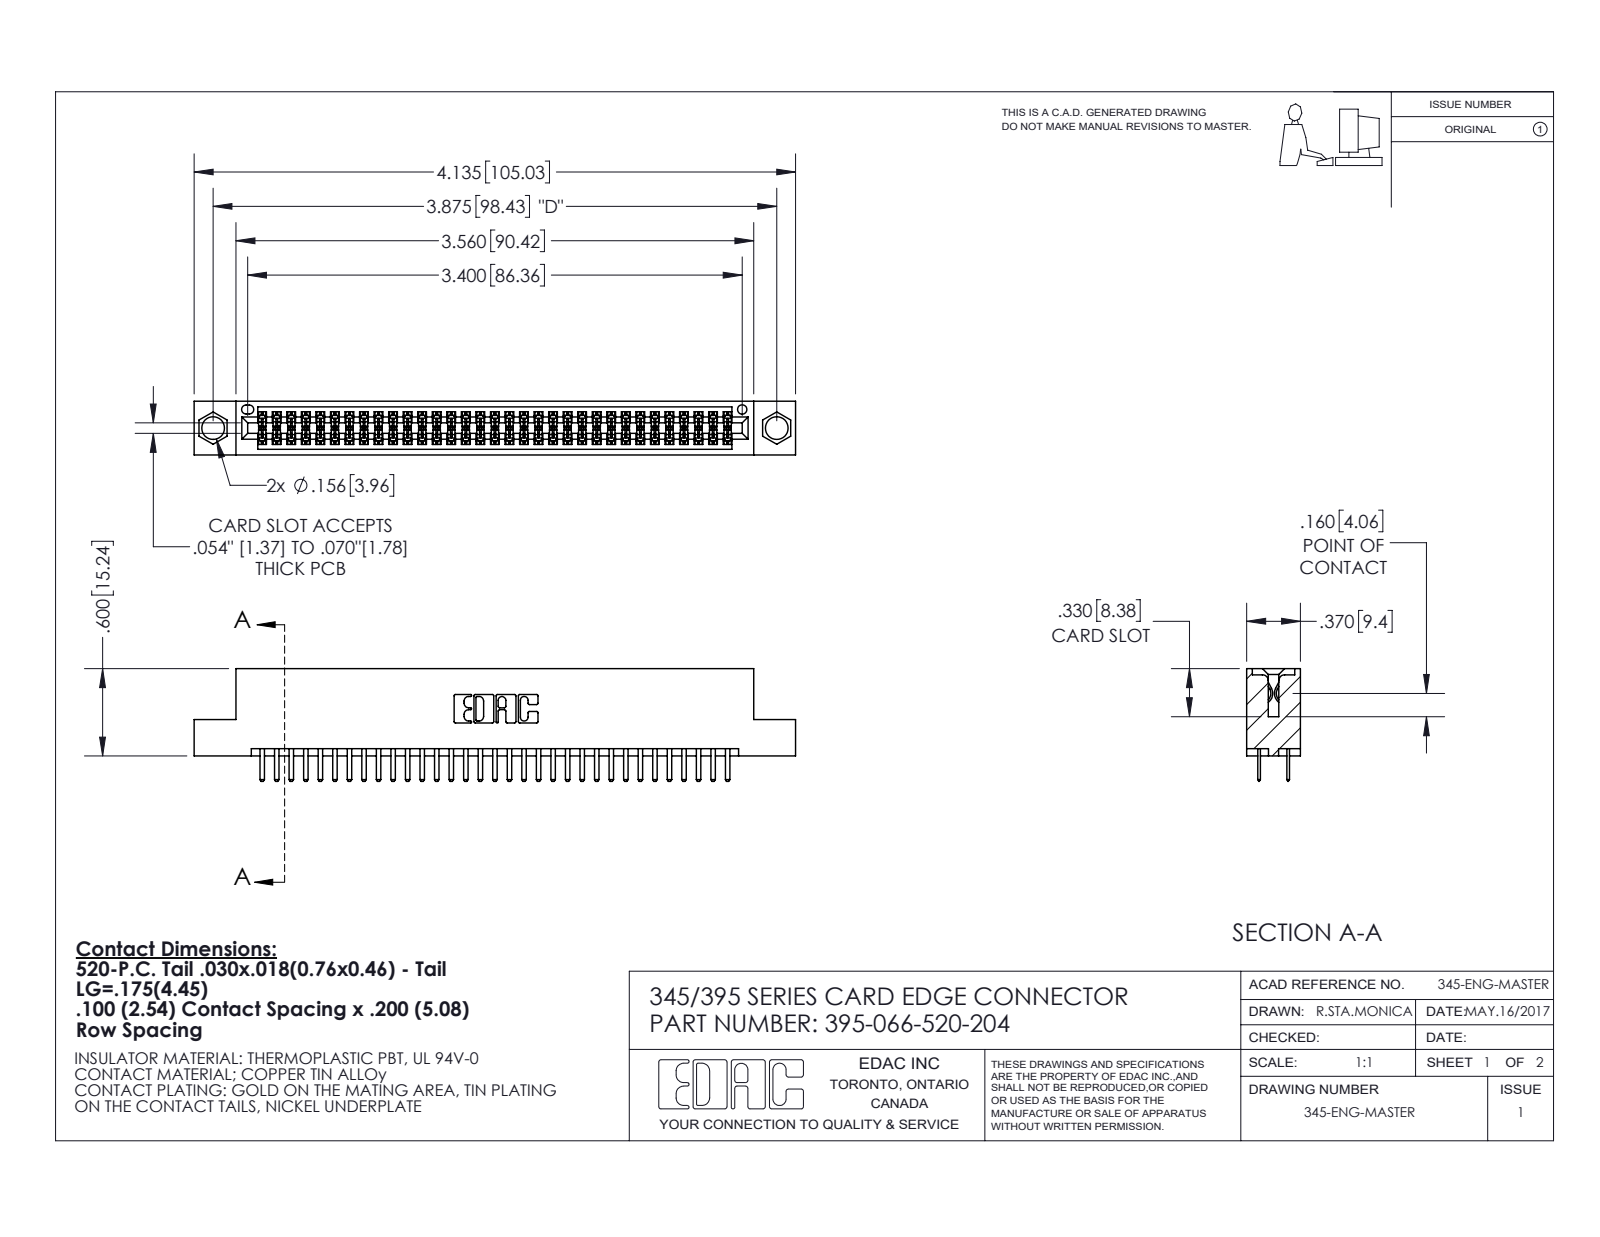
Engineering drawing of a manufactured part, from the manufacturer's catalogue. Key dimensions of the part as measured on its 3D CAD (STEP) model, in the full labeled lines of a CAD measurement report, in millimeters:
Part name (STEP PRODUCT): 345-292-001_345-293-120; 345 Part_Flush Mounting Lugs - 0.156 Dia-TI; 395-066-520-204
STEP written by: SolidWorks 2020 (CONFIG_CONTROL_DESIGN)
Units: millimetres
Bodies: 67 solids, 3704 faces (2404 planar, 1300 cylindrical, 0 other)
Overall size (bounding box): 105 × 19.7 × 9.4
Volume: 9 980 mm³ · Surface area: 14 370 mm²
Round holes (diameter × count): ⌀4 ×2, ⌀1.6 ×1
Partial cylindrical surfaces — rounded edges, fillets, slot ends (radius × count): R0.2 ×132, R0.3 ×70, R0.3 ×22, R0.2 ×6, R0.8 ×6, R0.7 ×3, R0.4 ×2, R0.5 ×2
Main face-to-face distances: 1.8, 7.6, 5.1, 9.4, 2.5, 6.9, 0.6, 5.7, 0.6, 1.8
Hole centre spacings: 6.9, 92.5, 98.4
